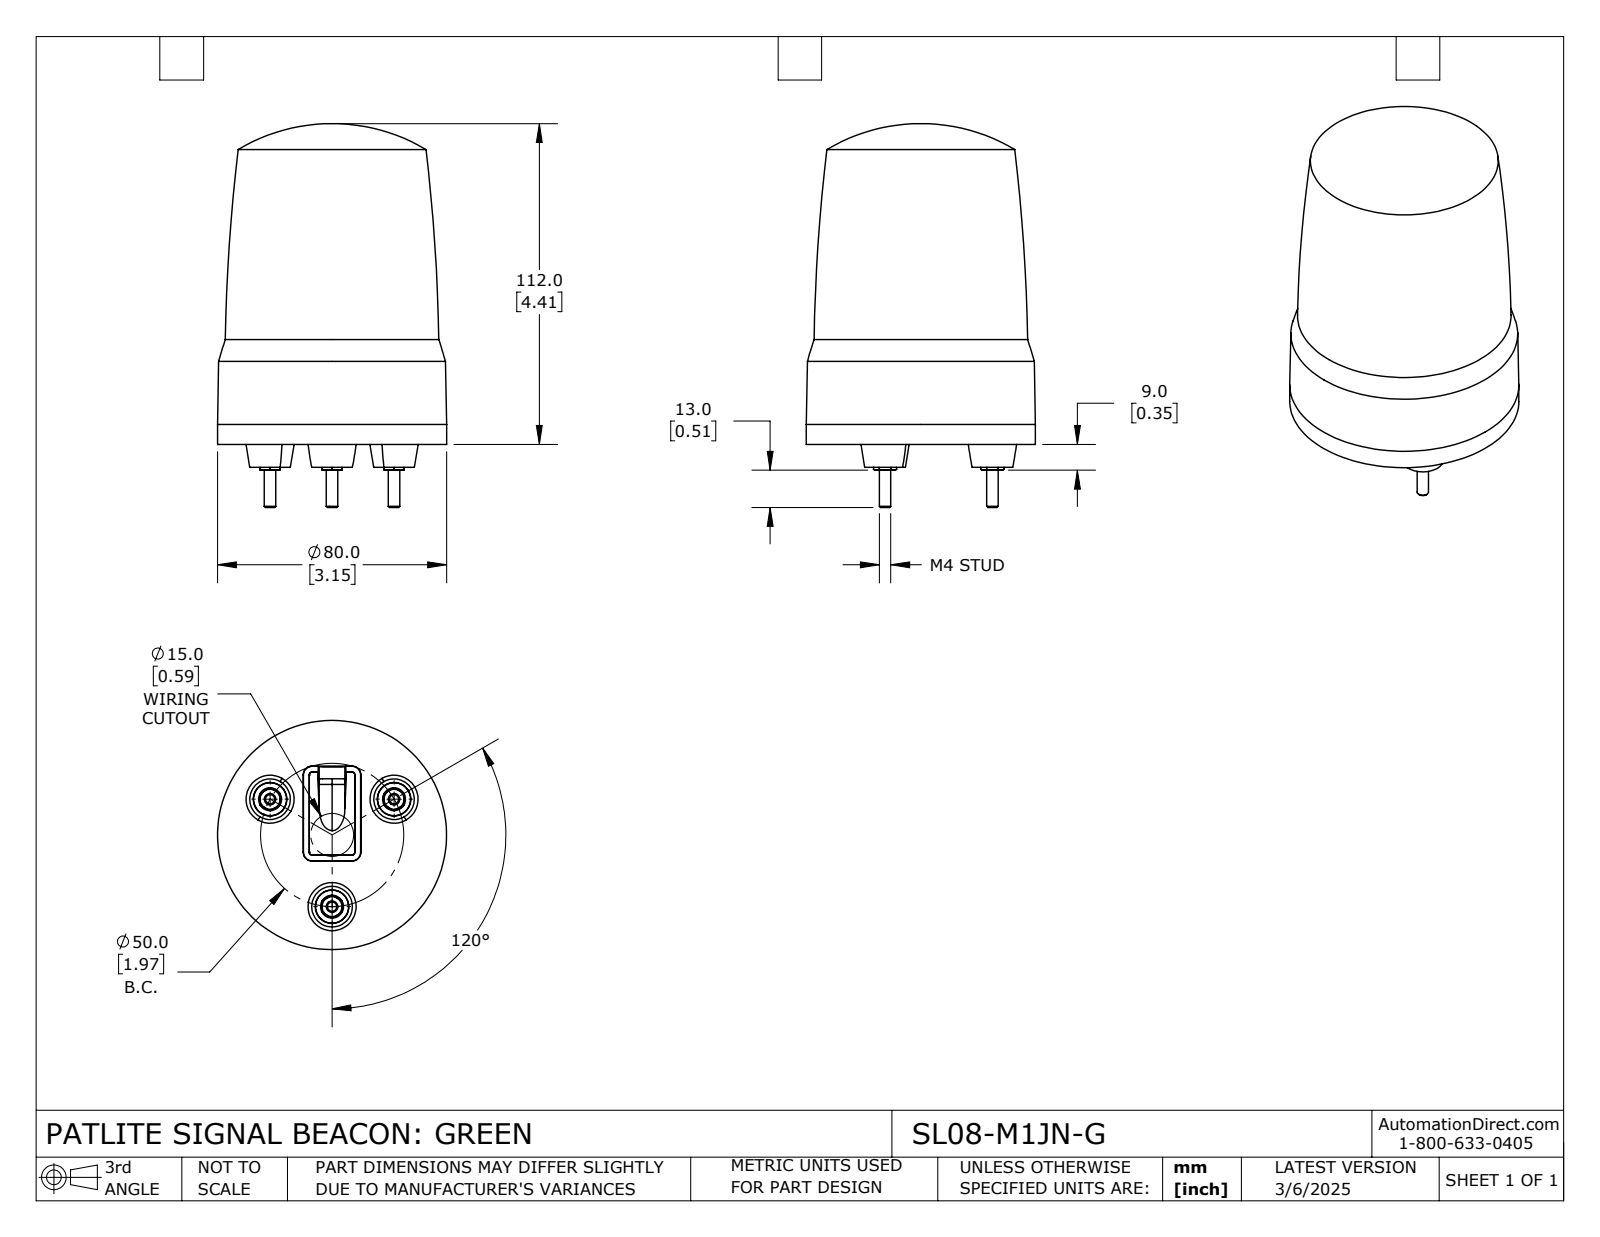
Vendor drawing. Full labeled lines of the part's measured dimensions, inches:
Part name (STEP PRODUCT): SL08-M1JN-G
STEP written by: SolidWorks 2024 (CONFIG_CONTROL_DESIGN)
Units: inches
Bodies: 1 solid, 138 faces (47 planar, 14 cylindrical, 77 other)
Overall size (bounding box): 5.276 × 3.15 × 3.15
Volume: 28.27 in³ · Surface area: 54.88 in²
Round bosses / shafts (diameter × count): ⌀0.315 ×3, ⌀0.157 ×3, ⌀3.15 ×1
Main face-to-face distances: 0.033, 0.096, 0.063, 0.209, 0.242, 0.305, 0.106, 0.315, 0.348, 0.411
